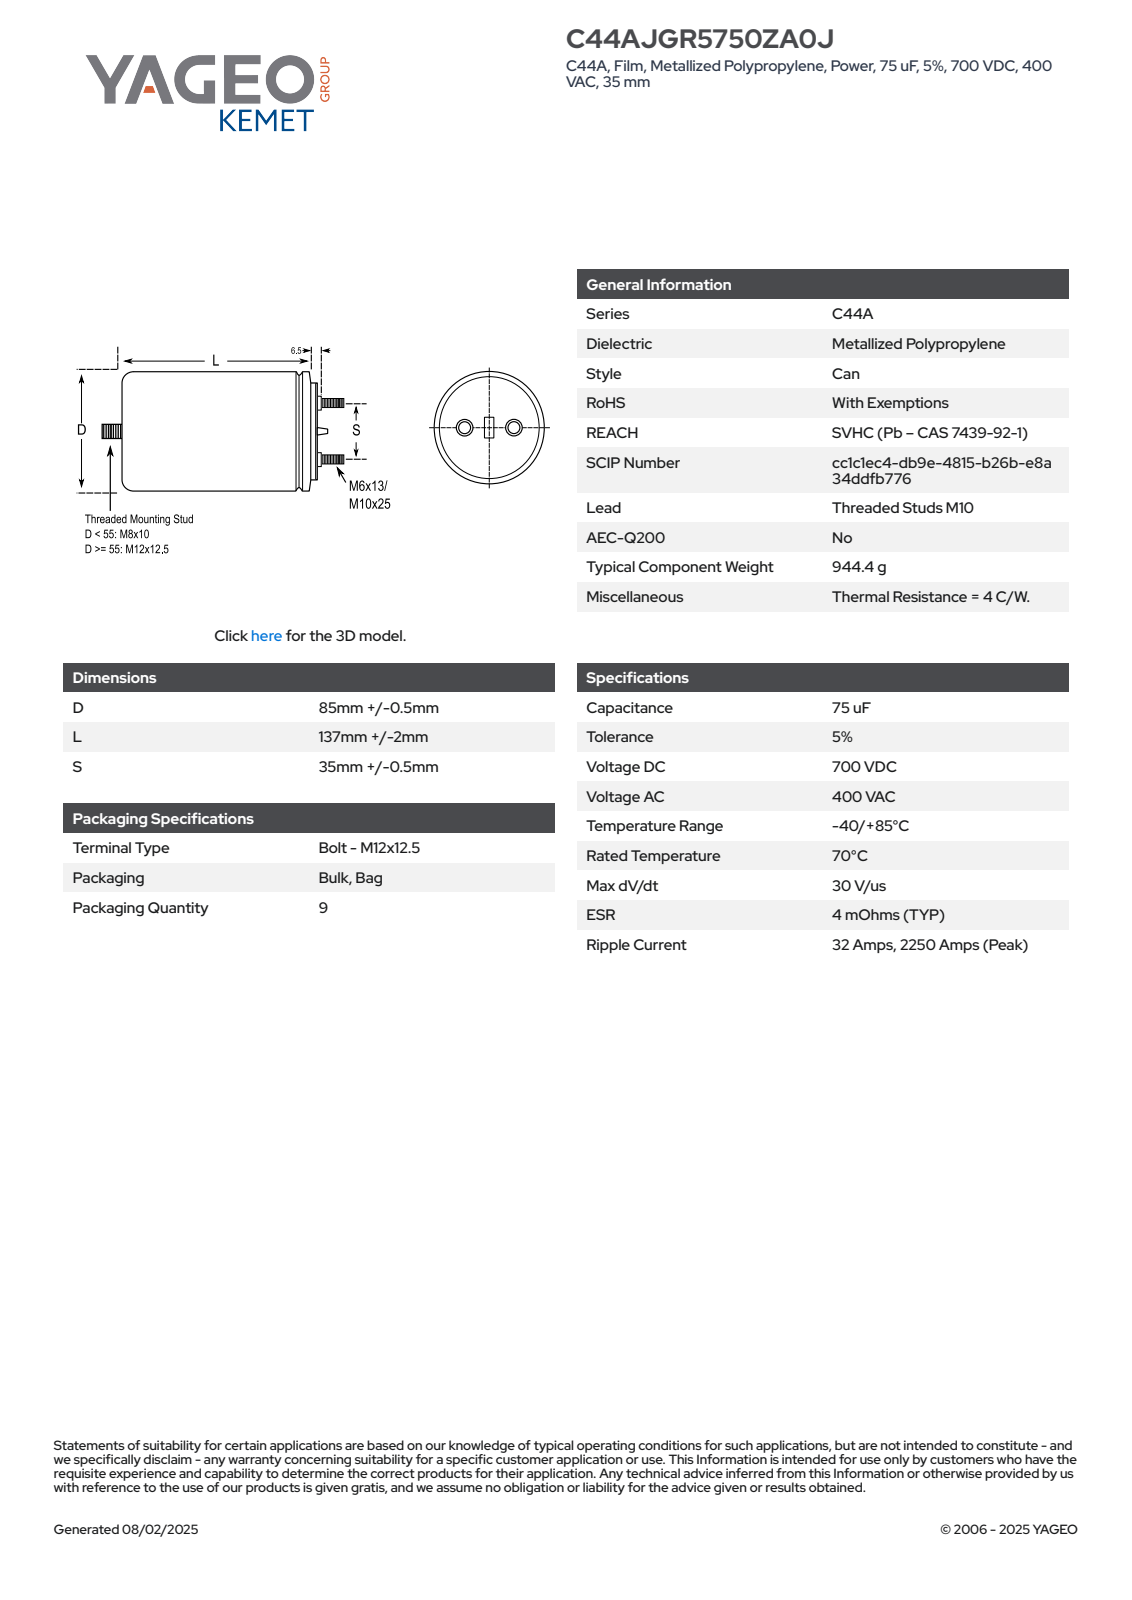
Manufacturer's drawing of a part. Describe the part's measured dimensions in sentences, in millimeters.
The part is named "CFP_C44A_85X137_D85.5L139S35". Its 3-D file was written by "SolidWorks 2014 (AUTOMOTIVE_DESIGN)". It is 1 solid with 102 faces: 29 planar, 34 cylindrical and 39 other. Overall it measures 171 by 85.5 by 85.5 millimeters. Its volume is 812 020 cubic millimeters and its surface area 50 663 square millimeters. Round bosses or shafts: 2 of diameter 9, 2 of diameter 6, 1 of diameter 85.5, 1 of diameter 67.06, 1 of diameter 12. Partial cylindrical surfaces (rounded edges, fillets, slot ends): 1 of radius 42.74. The main face-to-face distances are 144, 12.5, 156.5, 158, 145.5, 1.5, 171, 158.5, 14.5, 13.
